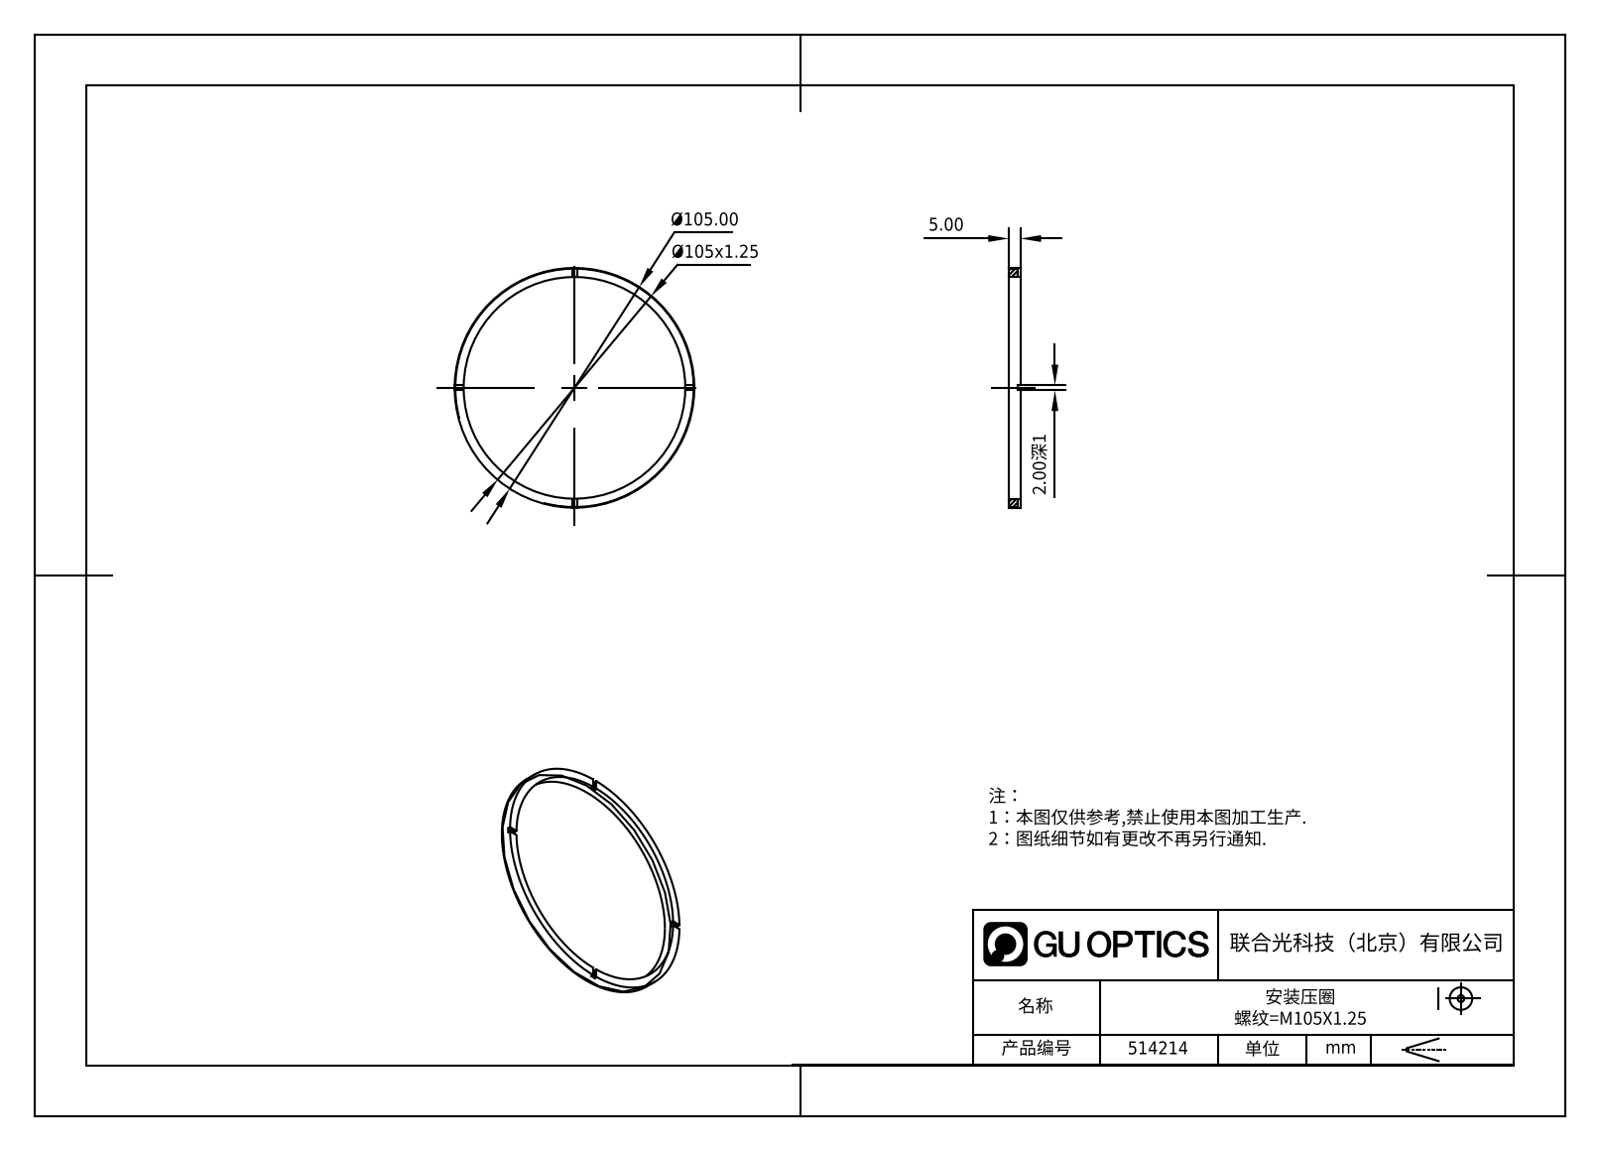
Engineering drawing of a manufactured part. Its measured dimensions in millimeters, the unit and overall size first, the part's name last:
Units: millimetres
Overall size (bounding box): 105 × 105 × 5
Round holes (diameter × count): ⌀97 ×1
Round bosses / shafts (diameter × count): ⌀105 ×1
Main face-to-face distances: 5, 4, 1, 2
Volume: 6 314 mm³ · Surface area: 5 727 mm²
Bodies: 1 solid, 21 faces (17 planar, 4 cylindrical, 0 other)
Part name (STEP PRODUCT): 514214
STEP written by: SolidWorks 2020 (CONFIG_CONTROL_DESIGN)
